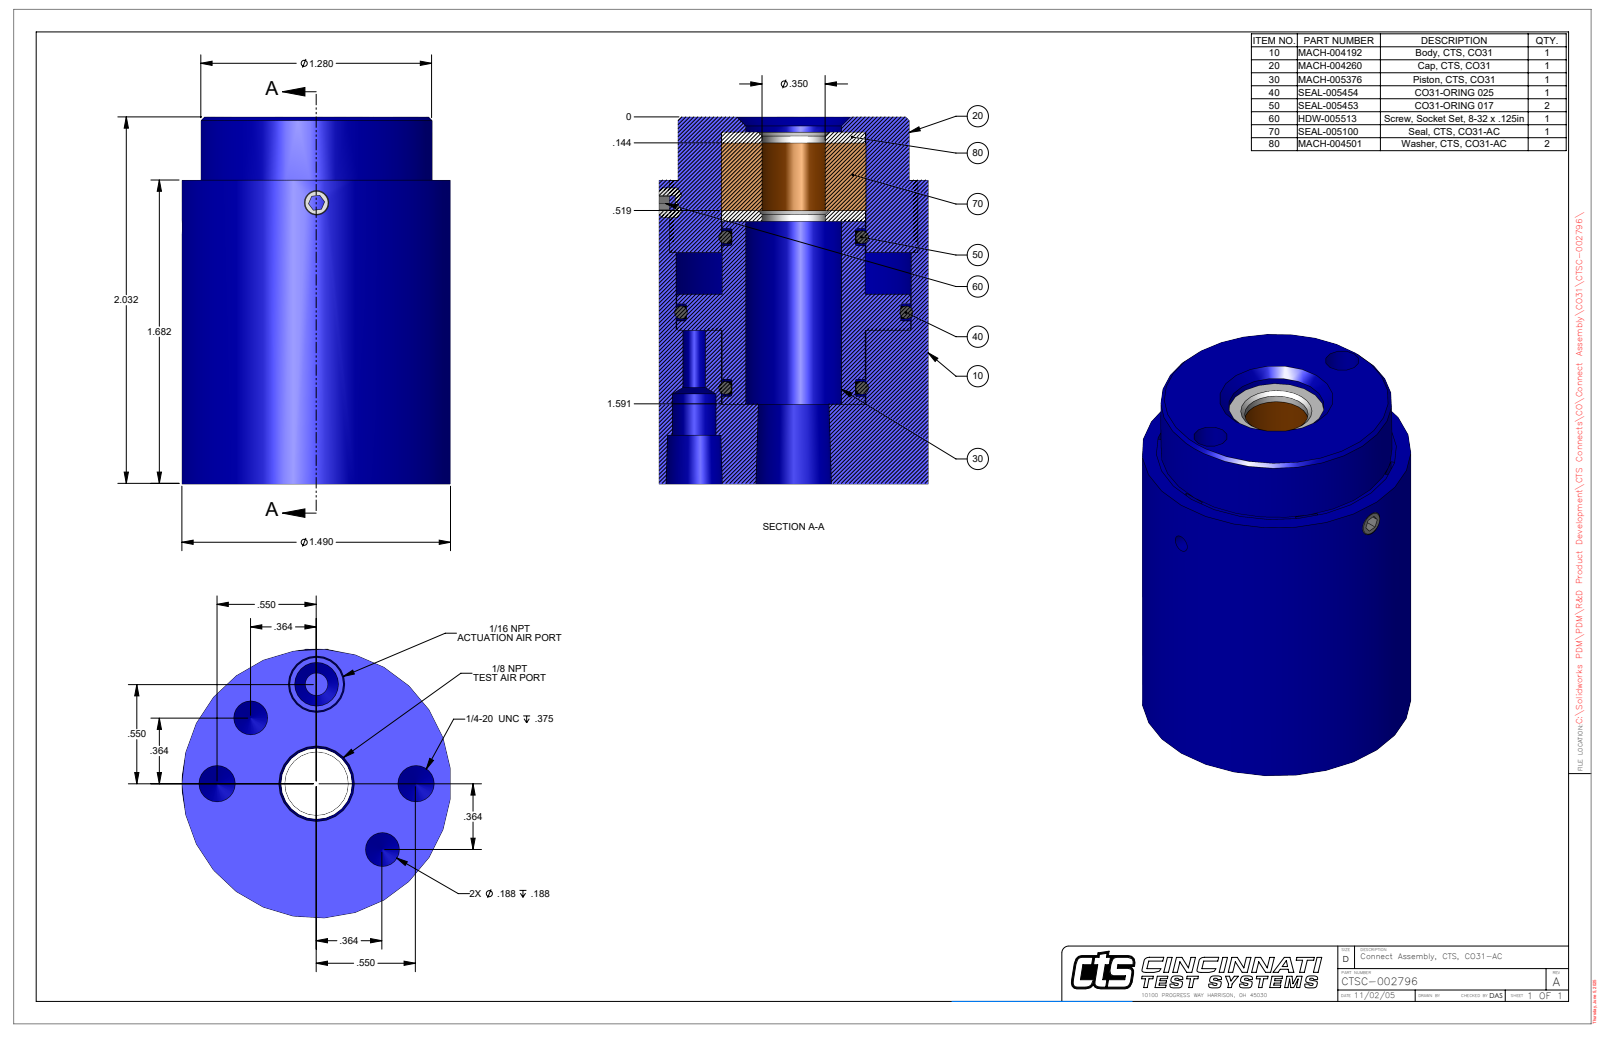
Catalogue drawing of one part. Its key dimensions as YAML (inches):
part_name: "CTSC-002796"
step_written_by: "SolidWorks 2023 (AUTOMOTIVE_DESIGN)"
units: inches
bodies: {solids: 1, faces: 111, planar: 53, cylindrical: 40, other: 18}
overall_size: [2.032, 1.49, 1.49]
volume: 2.972
surface_area: 17.07
round_holes:
  - {diameter: 0.187, count: 4}
  - {diameter: 0.201, count: 2}
  - {diameter: 0.094, count: 1}
  - {diameter: 0.136, count: 1}
  - {diameter: 0.242, count: 1}
  - {diameter: 0.35, count: 1}
  - {diameter: 0.352, count: 1}
  - {diameter: 0.53, count: 1}
  - {diameter: 0.8, count: 1}
  - {diameter: 1.33, count: 1}
round_bosses_or_shafts:
  - {diameter: 1.49, count: 1}
  - {diameter: 1.28, count: 1}
  - {diameter: 0.792, count: 1}
partial_cylinders:
  - {radius: 0.687, count: 1}
  - {radius: 0.731, count: 1}
face_to_face_distances: [2.032, 1.682, 0.35, 1.454, 0.228, 0.578, 0.301, 1.153, 1.381, 1.731]
hole_center_spacings: [0.515, 0.409, 0.55, 0.984, 0.035, 0.394, 0.754, 0.778]
